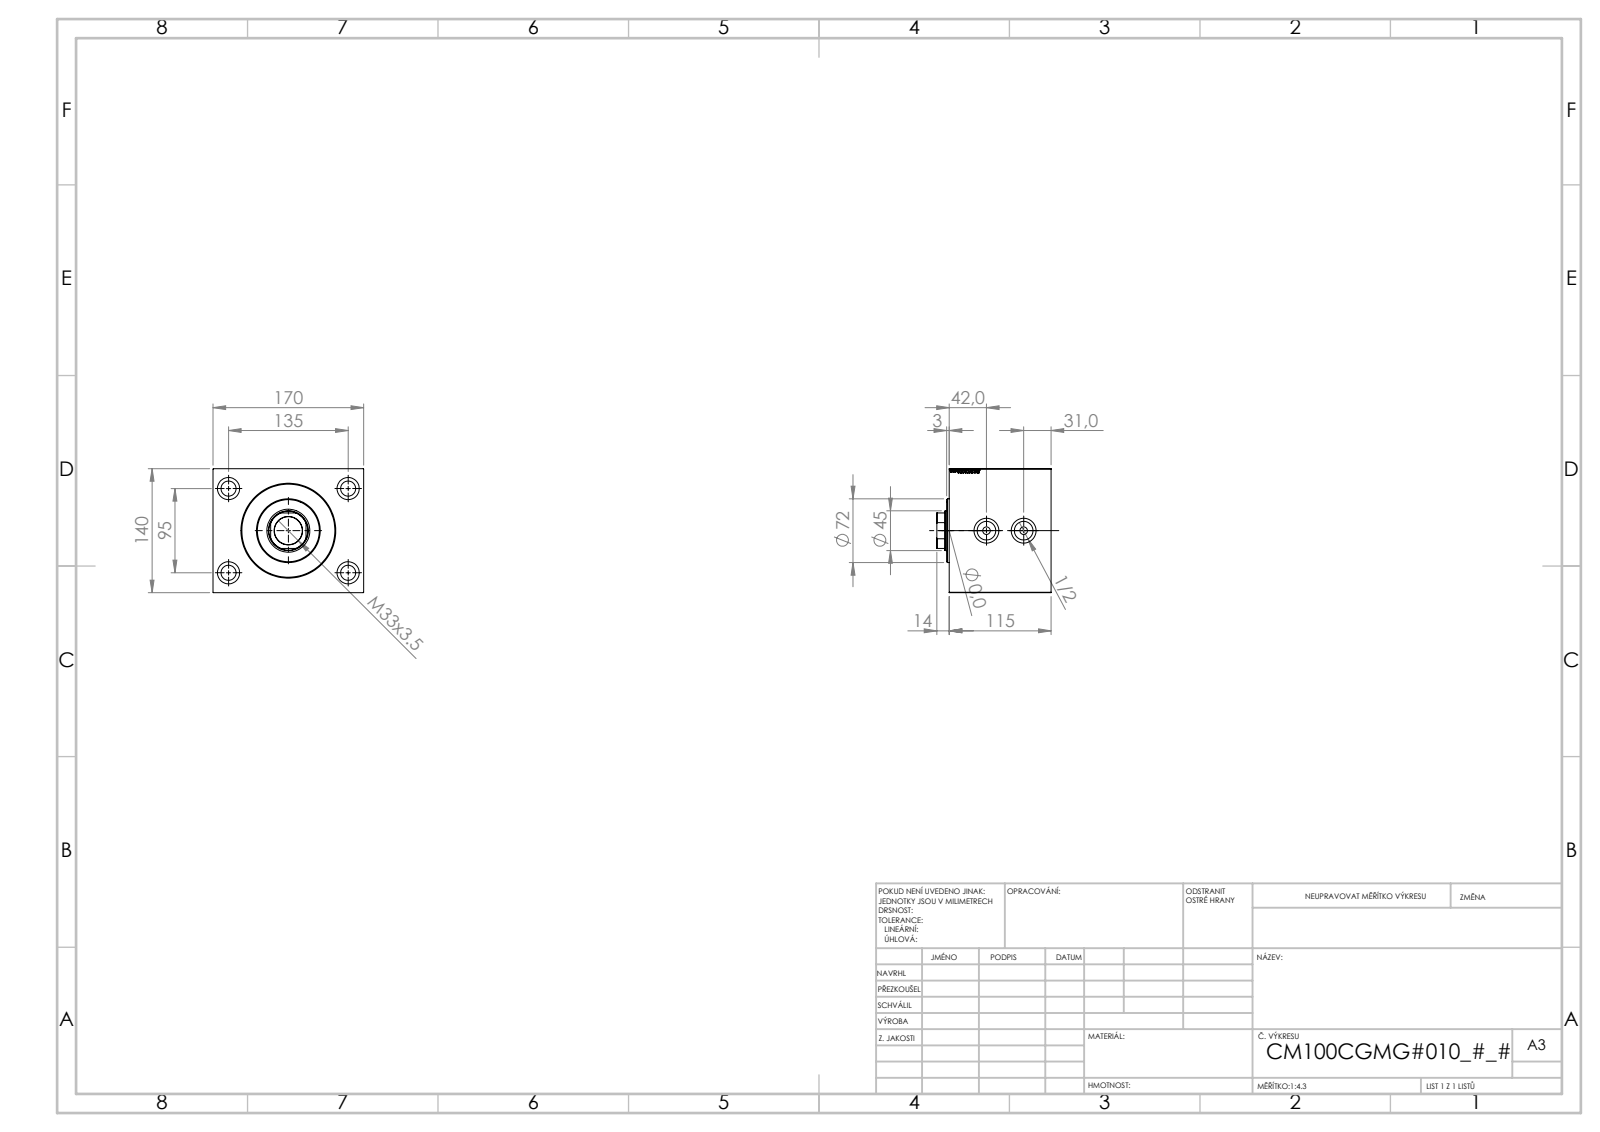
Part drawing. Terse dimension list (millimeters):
name: V450CM_C_VCP; V450CM_C_Body; V450CM_VC_B
written by: SolidWorks 2019 (CONFIG_CONTROL_DESIGN)
unit: mm
bodies: 3 solids, 866 faces (410 planar, 62 cylindrical, 394 other)
size: 170 × 140 × 130
volume: 2 516 000 mm³; area: 220 842 mm²
holes: 4× ⌀17, 4× ⌀25, 2× ⌀8.5, 2× ⌀20.96, 2× ⌀28, 1× ⌀31.5, 1× ⌀45, 1× ⌀48.5, 1× ⌀100, 1× ⌀102, 1× ⌀105
bosses: 1× ⌀72
rounds: 1× R22
face distances: 140, 115, 53.75, 61.25, 170, 10, 20, 105, 43.75, 33.75
hole spacings: 82.54, 95, 135, 165.08, 42
